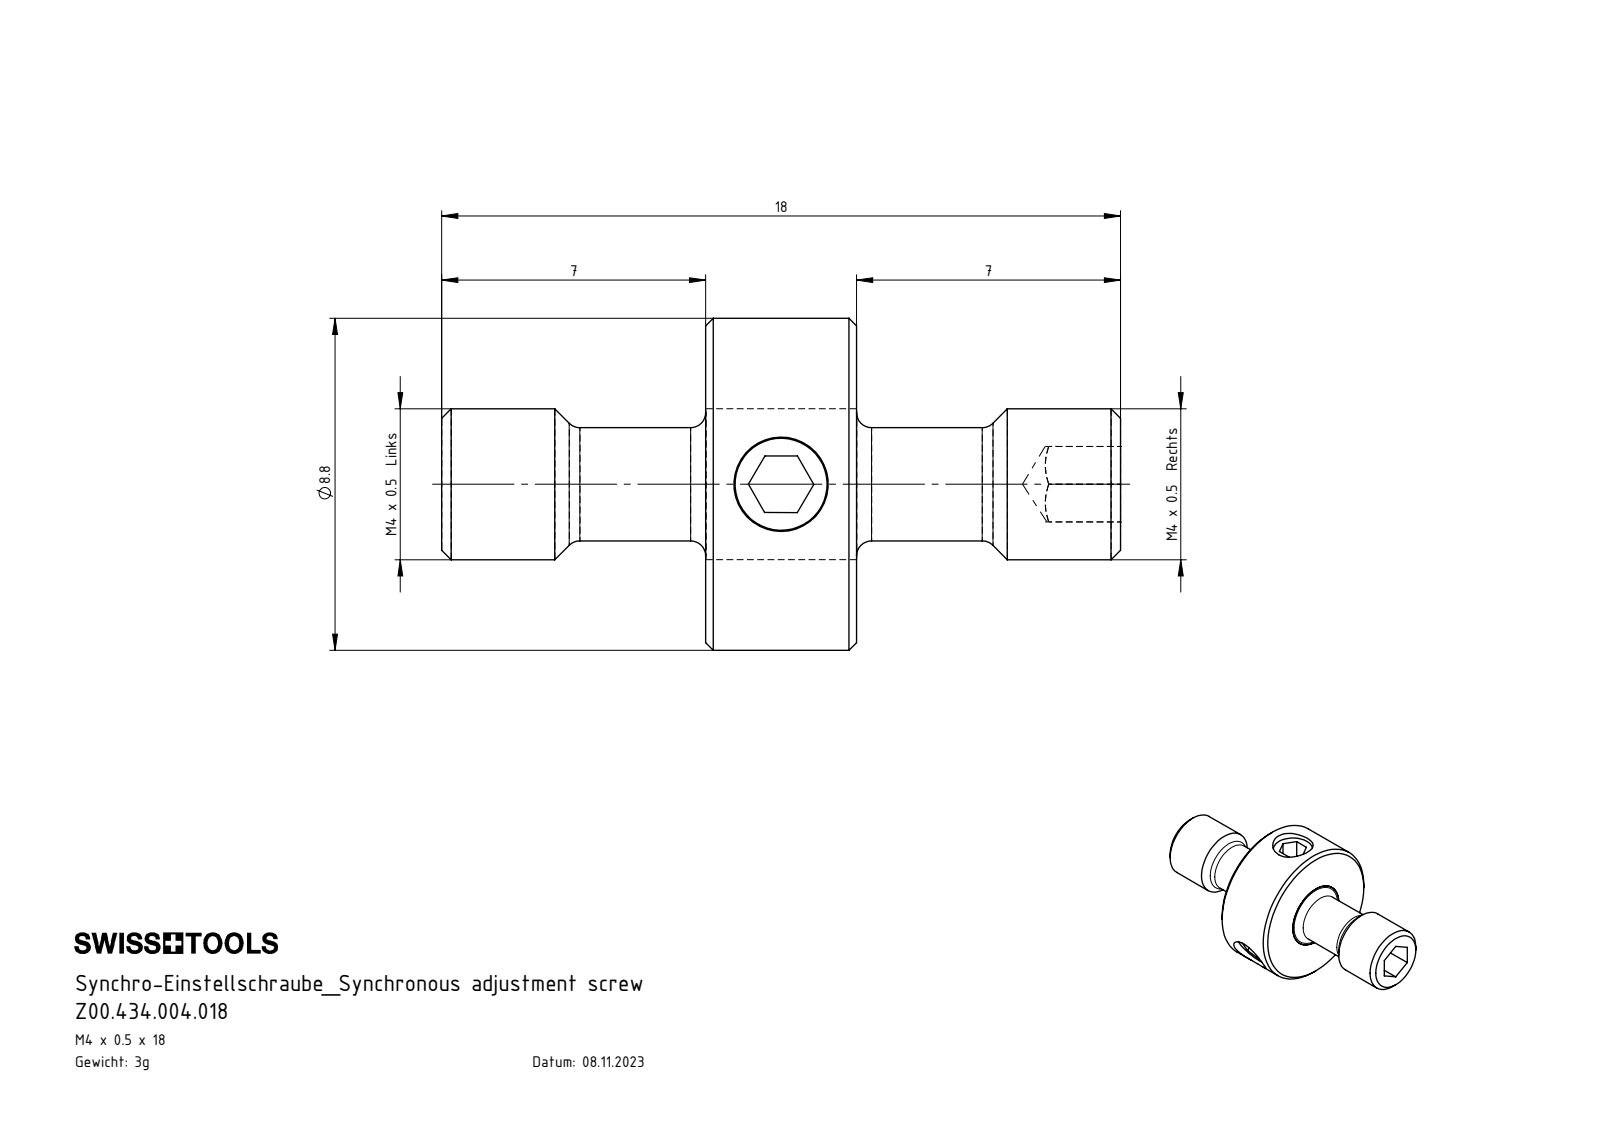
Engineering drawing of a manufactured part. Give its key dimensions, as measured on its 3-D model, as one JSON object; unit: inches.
{"part_name": "Z00.434.004.018; Z20-ER3.002.004_A; Z20-ER3.001.018_A; ISO 4026 - M3 x 2", "step_written_by": "SolidWorks 2022 (AUTOMOTIVE_DESIGN)", "units": "inches", "bodies": {"solids": 5, "faces": 96, "planar": 36, "cylindrical": 26, "other": 34}, "overall_size": [0.709, 0.346, 0.346], "volume_in3": 0.022, "surface_area_in2": 0.986, "round_holes": [[0.098, 3]], "round_bosses_or_shafts": [[0.118, 4], [0.346, 1], [0.157, 1]], "face_to_face_distances": [0.157, 0.276, 0.433, 0.059, 0.079, 0.709]}
